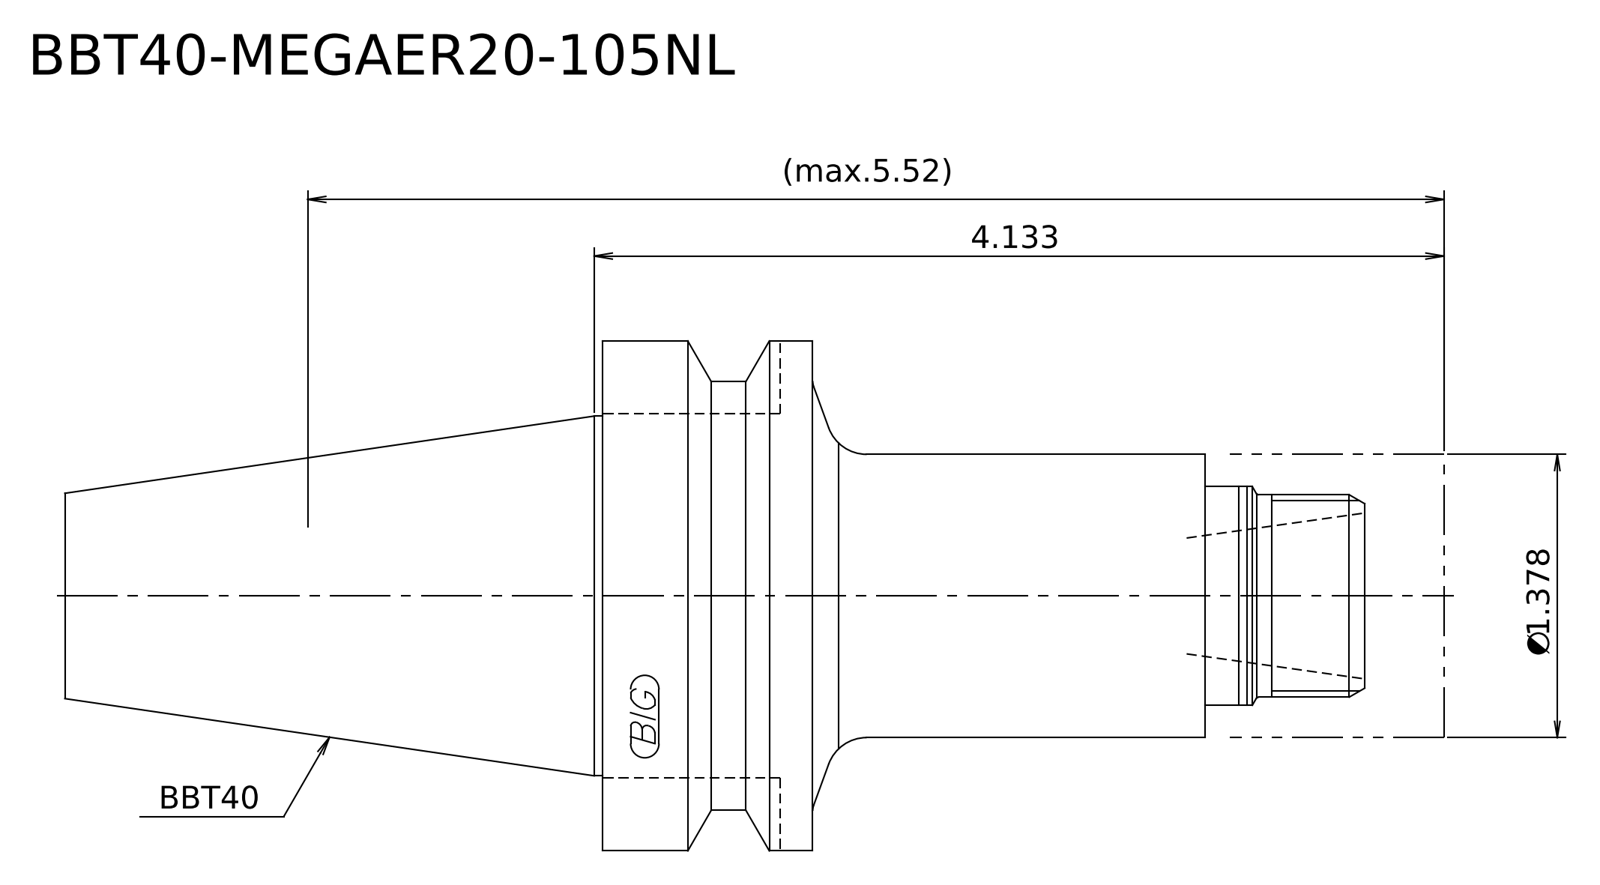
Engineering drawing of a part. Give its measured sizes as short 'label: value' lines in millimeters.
written by: Kubotek KeyCreator 2011 V10.0.2 (22737) (automotive_design)
unit: mm
bodies: 2 solids, 21 faces (7 planar, 8 cylindrical, 6 other)
size: 170.4 × 63 × 63
volume: 226 279 mm³; area: 29 775 mm²
bosses: 1× ⌀63, 1× ⌀53, 1× ⌀44.45, 1× ⌀35, 1× ⌀27, 1× ⌀25
face distances: 77.5, 26.5, 104, 78, 51.5, 26, 170.4, 143.9, 92.4, 66.4
